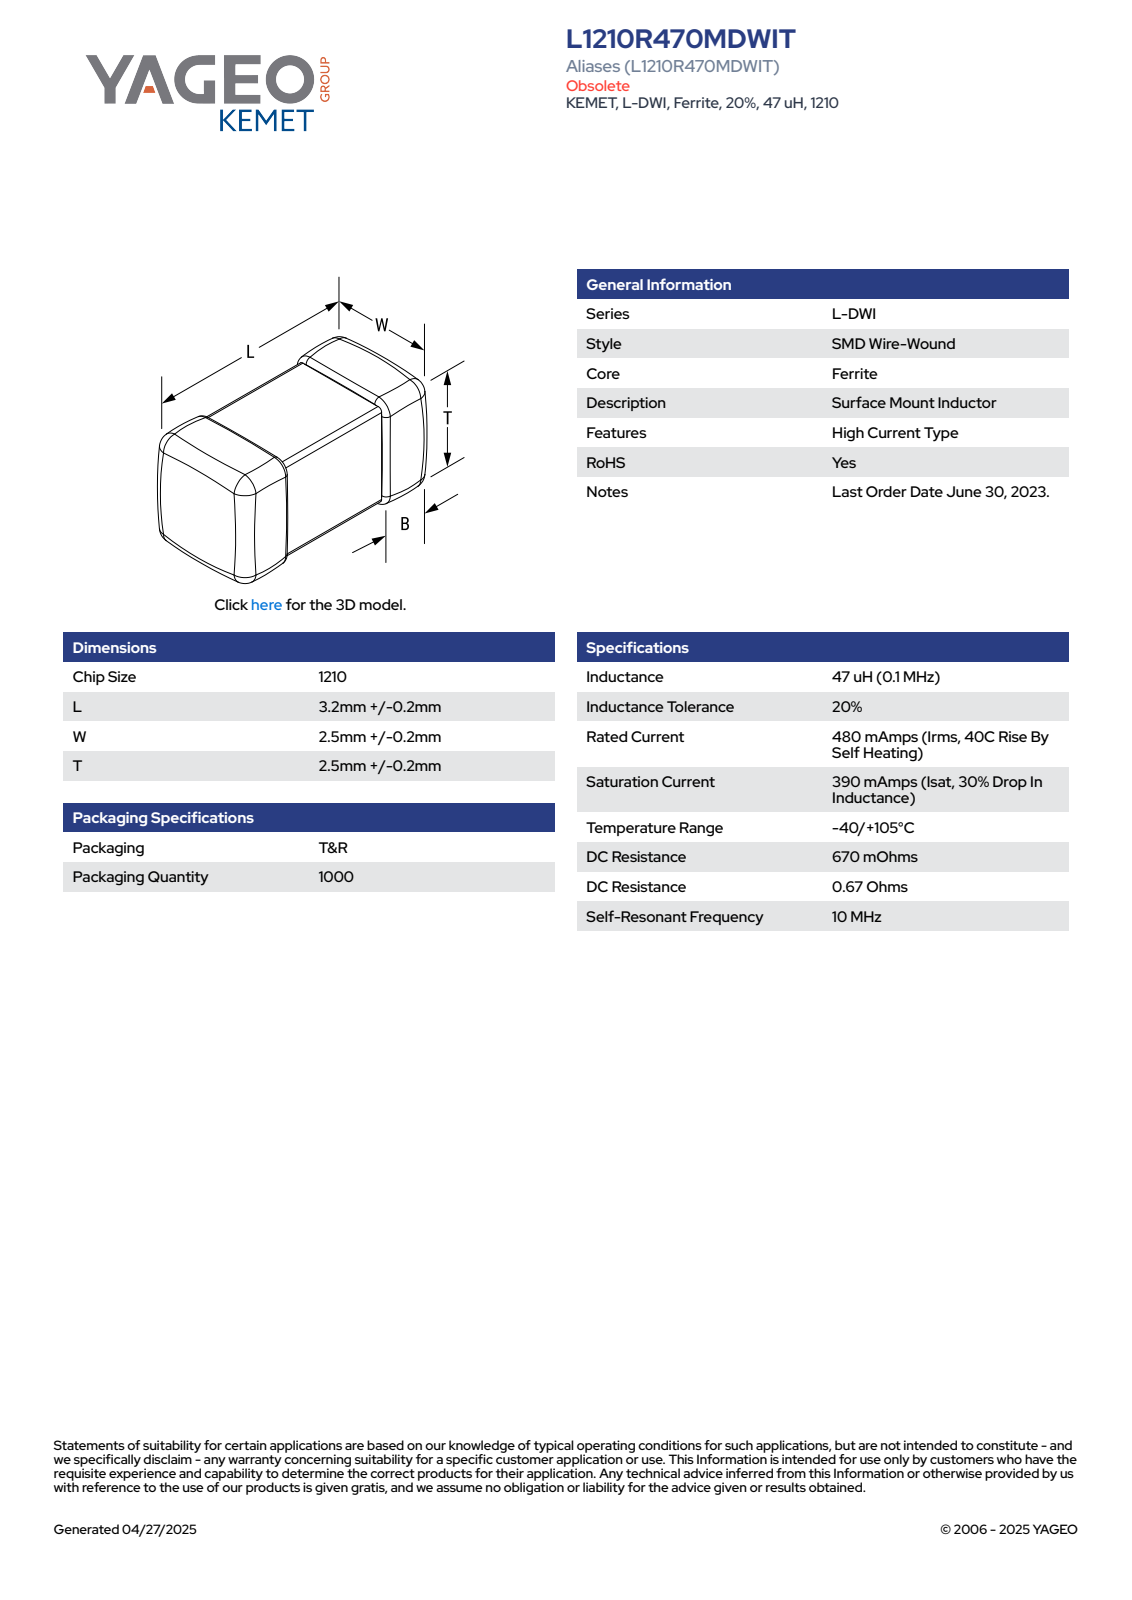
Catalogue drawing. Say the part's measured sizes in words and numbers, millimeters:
The part is named "IS_KC_1210_L3.4W2.7T2.7LL0.9". Its 3-D file was written by "SolidWorks 2014 (AUTOMOTIVE_DESIGN)". It is 4 solids with 73 faces: 73 planar, 0 cylindrical and 0 other. Overall it measures 3.4 by 2.7 by 2.7 millimeters. Its volume is 24 cubic millimeters and its surface area 53 square millimeters. The main face-to-face distances are 2.65, 2.7, 2.6, 3.4, 0.9, 2.5, 1.6, 2.66, 2.61, 0.95.
